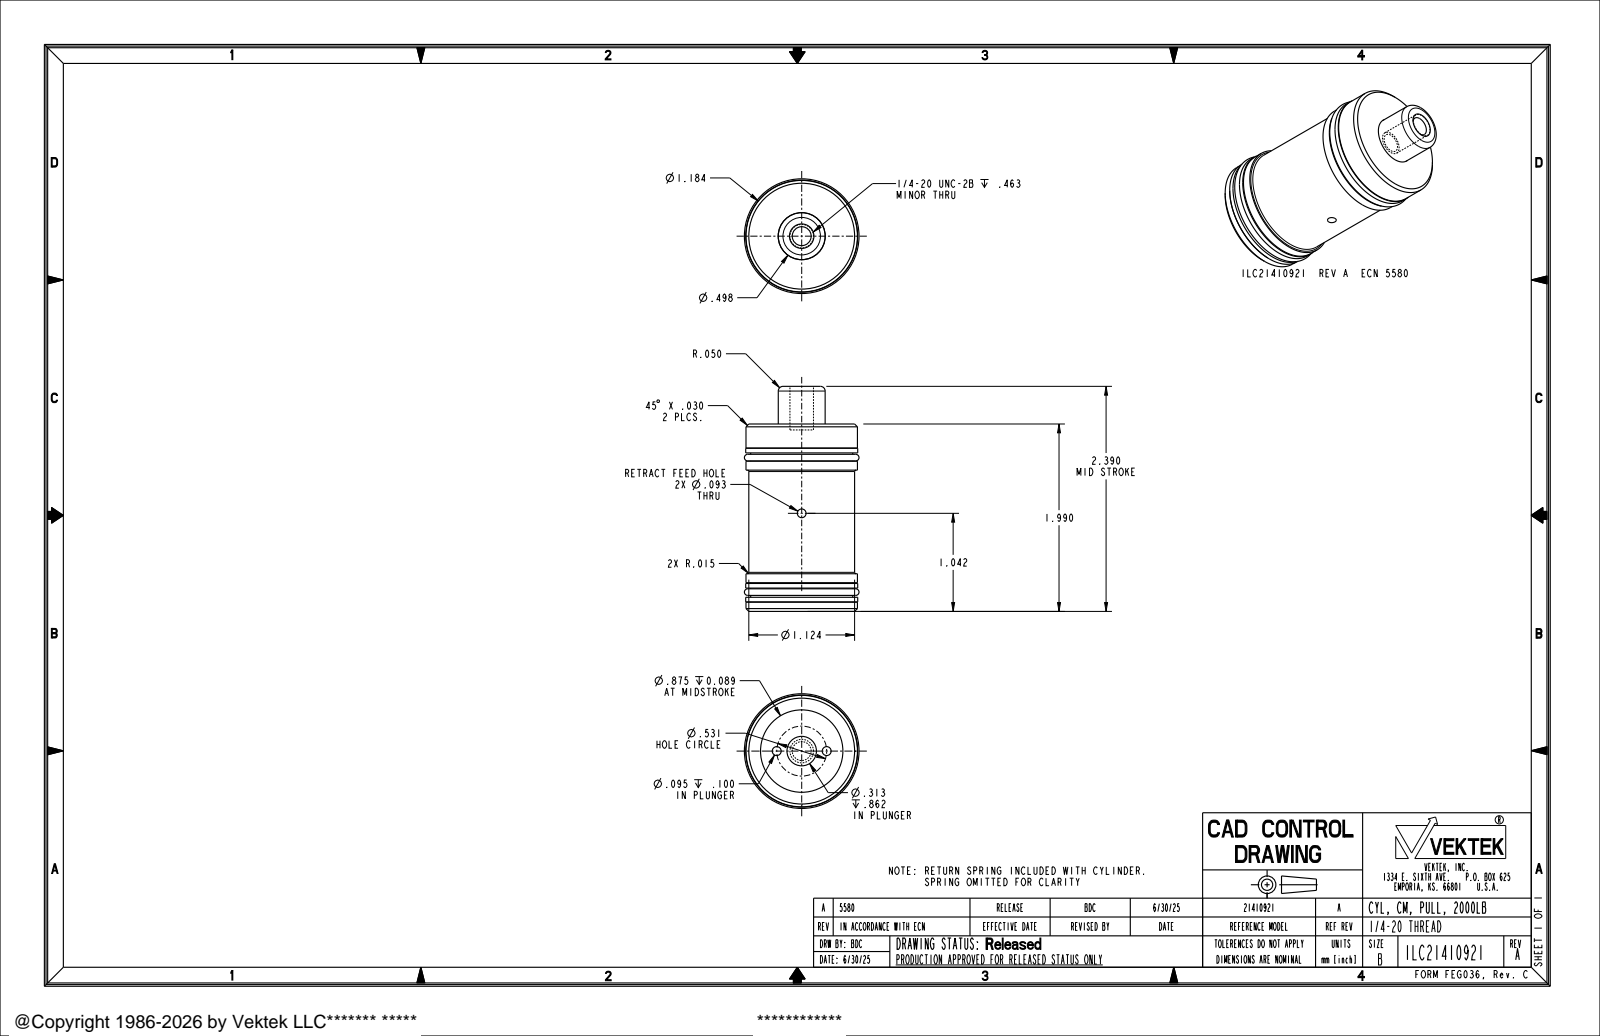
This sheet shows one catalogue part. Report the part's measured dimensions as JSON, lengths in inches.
{"part_name": "ILC21410921_BODY; ILC21410921_PLUNGER; ILC21410921", "step_written_by": "CREO PARAMETRIC BY PTC INC, 2021164 (AUTOMOTIVE_DESIGN)", "units": "inches", "bodies": {"solids": 2, "faces": 91, "planar": 23, "cylindrical": 52, "other": 16}, "overall_size": [2.39, 1.218, 1.218], "volume_in3": 1.732, "surface_area_in2": 23.08, "round_holes": [[0.095, 2], [0.093, 1], [0.201, 1], [0.313, 1], [0.5, 1], [0.875, 1]], "round_bosses_or_shafts": [[1.19, 1], [1.184, 1], [1.124, 1], [1.084, 1], [0.498, 1], [0.25, 1]], "face_to_face_distances": [1.675, 1.99, 1.212, 0.463, 0.897, 0.315, 0.778, 1.093, 0.778, 0.315], "hole_center_spacings": [0.265, 0.531]}
